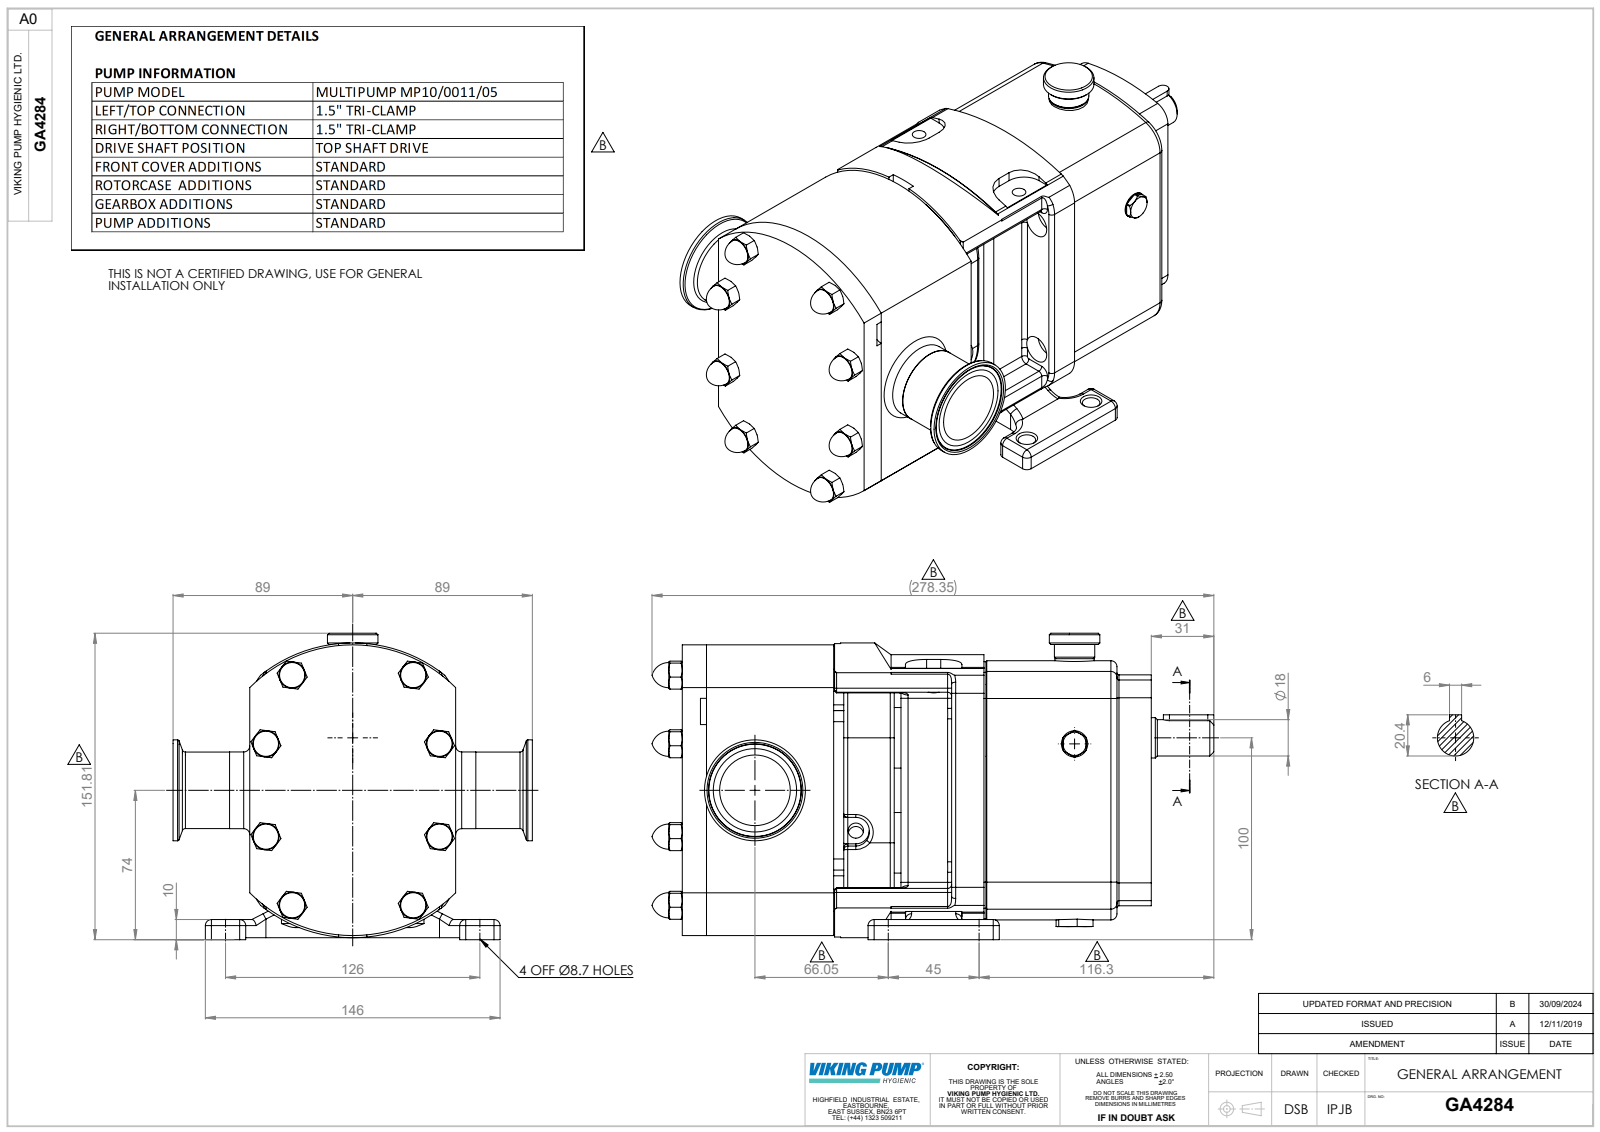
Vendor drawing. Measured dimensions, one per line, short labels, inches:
name: Copy of Z94-5121-22 - 1.5 INCH^GA4284; GA4284; Copy of CP10-0011-05 H T^GA4284
written by: SolidWorks 2023 (AUTOMOTIVE_DESIGN)
unit: in
bodies: 3 solids, 762 faces (252 planar, 218 cylindrical, 292 other)
size: 10.959 × 7.008 × 5.977
volume: 159.3 in³; area: 305 in²
holes: 4× ⌀0.343, 4× ⌀0.551, 2× ⌀0.268, 2× ⌀0.3, 1× ⌀0.887, 1× ⌀1.378
bosses: 2× ⌀1.181, 1× ⌀1.969, 1× ⌀1.496, 1× ⌀1.492, 1× ⌀0.985, 1× ⌀0.787, 1× ⌀0.787, 1× ⌀0.768
rounds: 30× R0.079, 26× R0.118, 12× R0.531, 8× R0.413, 6× R0.138, 4× R0.217, 4× R0.236, 4× R0.354
face distances: 0.197, 4.016, 9.148, 4.882, 3.819, 0.197, 3.622, 3.819, 4.266, 4.134
hole spacings: 1.414, 3.959, 1.772, 2.992, 3.032, 4.26, 4.961, 5.267
